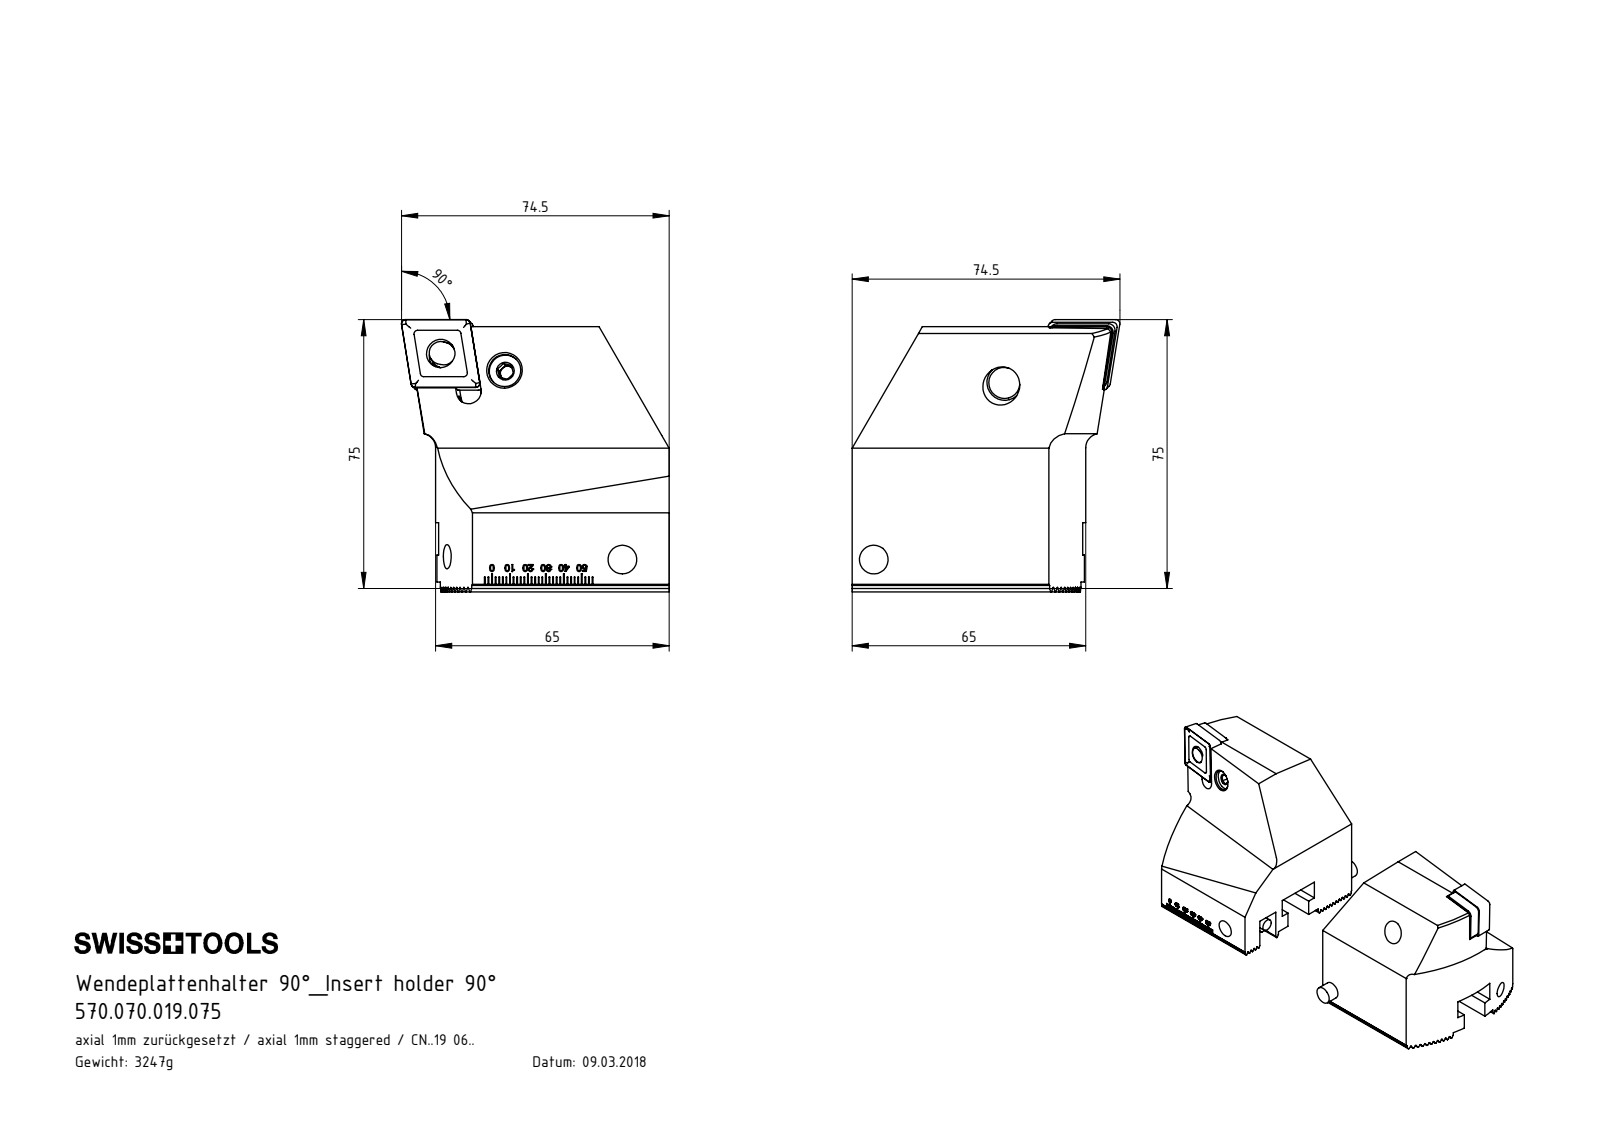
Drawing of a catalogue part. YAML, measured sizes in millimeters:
part_name: "ISO 4028 - M8 x 35; WCF-ER3.101.000_A; WCF; VK1-WCF.101.075_A (+6 more)"
step_written_by: "SolidWorks 2017 (CONFIG_CONTROL_DESIGN)"
units: millimeters
bodies: {solids: 16, faces: 1300, planar: 784, cylindrical: 170, other: 346}
overall_size: [200.04, 83.92, 75.79]
volume: 410334
surface_area: 73404
round_holes:
  - {diameter: 8, count: 4}
  - {diameter: 6.8, count: 2}
  - {diameter: 7.94, count: 2}
  - {diameter: 9, count: 2}
  - {diameter: 9.6, count: 2}
  - {diameter: 10.2, count: 2}
round_bosses_or_shafts:
  - {diameter: 10, count: 2}
  - {diameter: 9.9, count: 2}
  - {diameter: 8.6, count: 2}
  - {diameter: 8, count: 2}
  - {diameter: 5.5, count: 2}
  - {diameter: 4.45, count: 2}
partial_cylinders:
  - {radius: 0.14, count: 22}
  - {radius: 1.2, count: 8}
  - {radius: 1.8, count: 8}
  - {radius: 4.15, count: 8}
  - {radius: 4.7, count: 3}
  - {radius: 3.1, count: 2}
  - {radius: 3.5, count: 2}
  - {radius: 3.65, count: 2}
face_to_face_distances: [1.73, 6.93, 8.66, 70, 3.46, 5.2, 41.57, 43.3, 24.5, 45.5]
hole_center_spacings: [7, 18.52, 70, 0.31, 0.32, 18.8, 18.81, 40]
